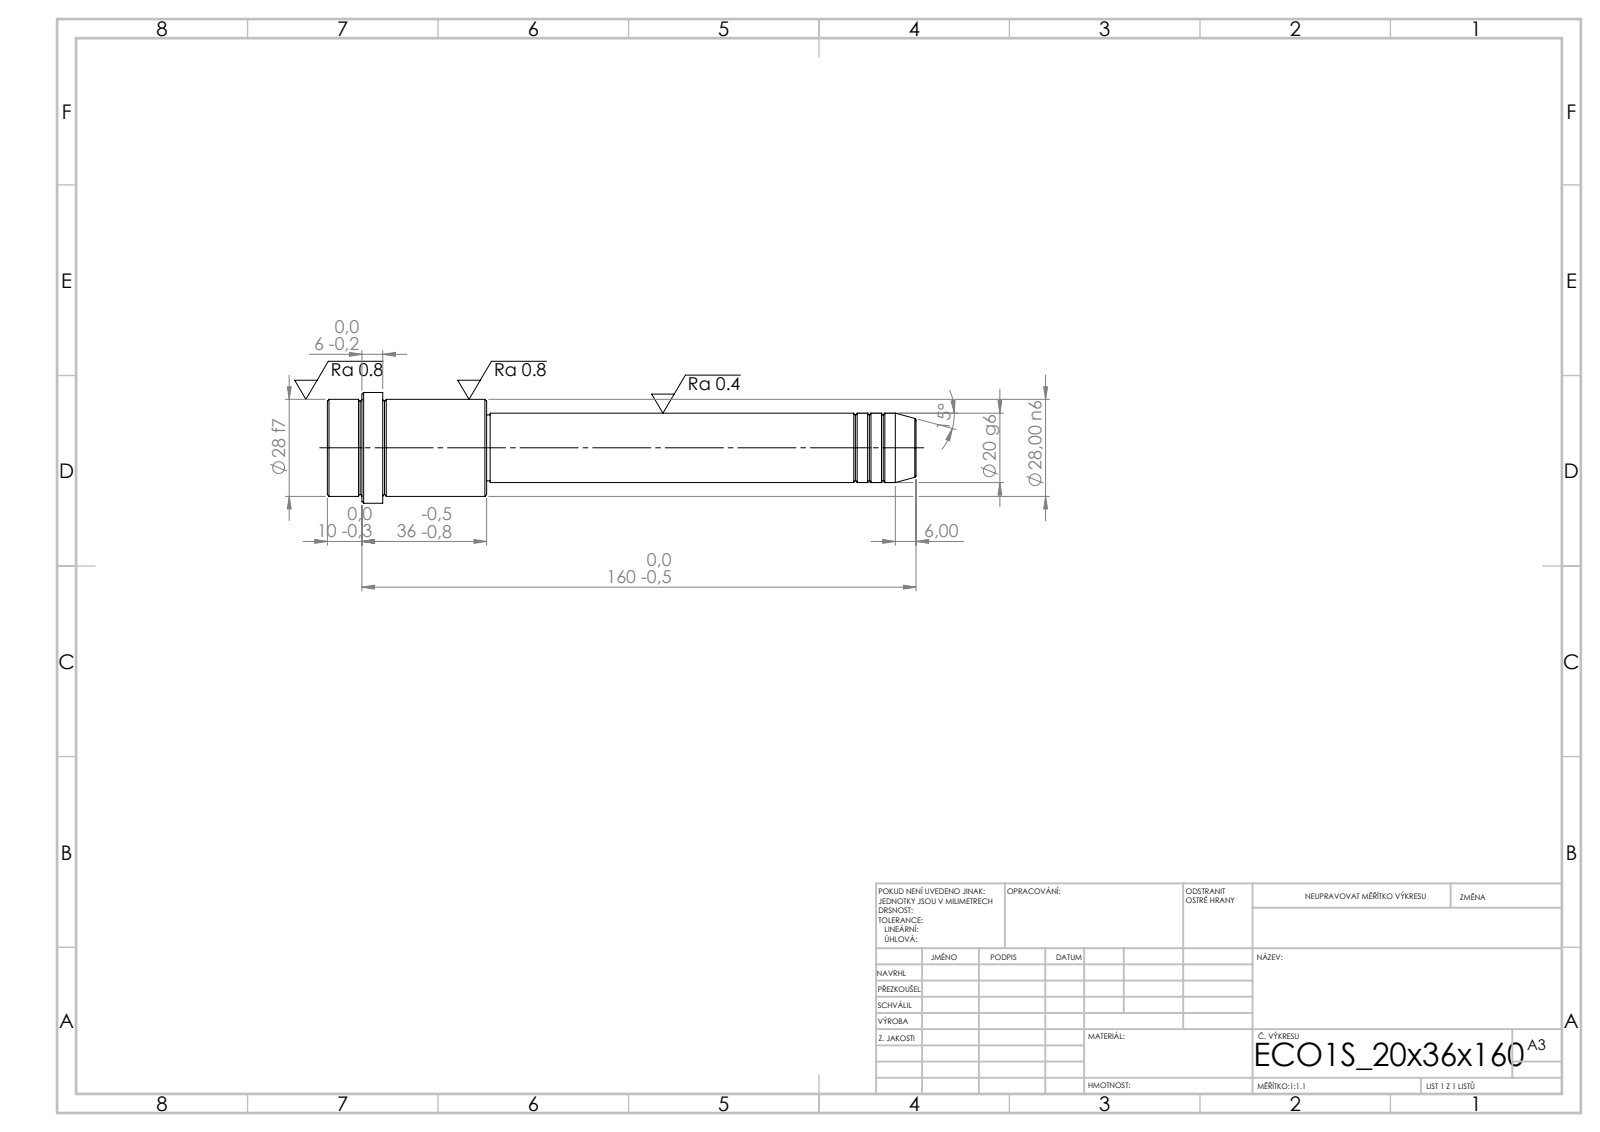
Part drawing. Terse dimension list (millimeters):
written by: SolidWorks 2019 (CONFIG_CONTROL_DESIGN)
unit: mm
bodies: 1 solid, 52 faces (6 planar, 16 cylindrical, 30 other)
size: 170 × 32 × 32
volume: 67 918 mm³; area: 13 573 mm²
bosses: 1× ⌀32, 1× ⌀28, 1× ⌀20, 1× ⌀19
face distances: 46, 124, 170, 154, 30, 16, 160, 36, 6, 10
